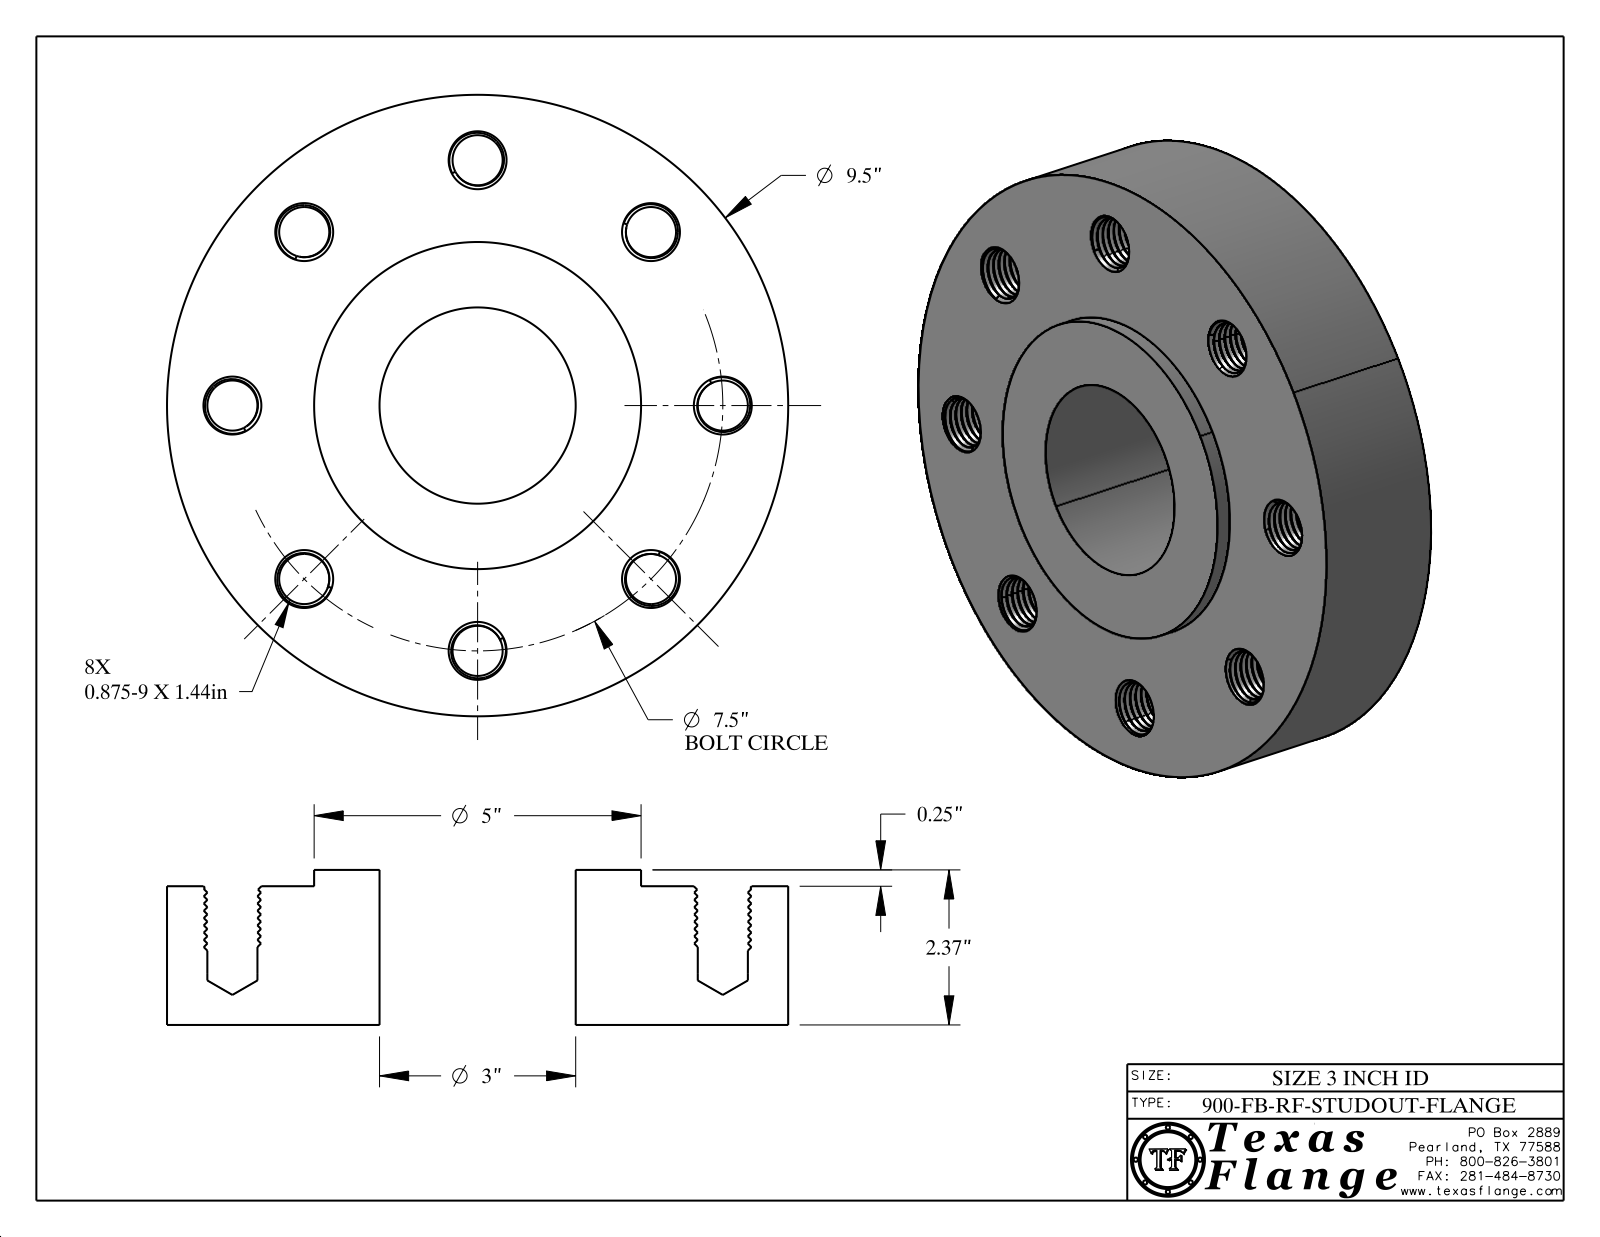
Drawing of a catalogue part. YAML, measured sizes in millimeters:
part_name: "3-900-FB-RF-STUDOUT-FLANGE"
step_written_by: "CATIA V5 STEP AP214 (AUTOMOTIVE_DESIGN)"
units: millimeters
bodies: {solids: 1, faces: 874, planar: 368, cylindrical: 186, other: 320}
overall_size: [241.3, 241.3, 60.2]
volume: 2168000
surface_area: 163700
round_holes:
  - {diameter: 19.5, count: 8}
  - {diameter: 25.4, count: 1}
  - {diameter: 76.2, count: 1}
round_bosses_or_shafts:
  - {diameter: 1.5, count: 8}
  - {diameter: 241.3, count: 1}
  - {diameter: 127, count: 1}
  - {diameter: 20, count: 1}
face_to_face_distances: [53.8, 6.4, 60.2, 59.8, 53.5, 0.4, 7.6, 7.4, 1.4, 6.3]
hole_center_spacings: [72.9, 95.3, 134.7, 176, 190.5, 190.5]
